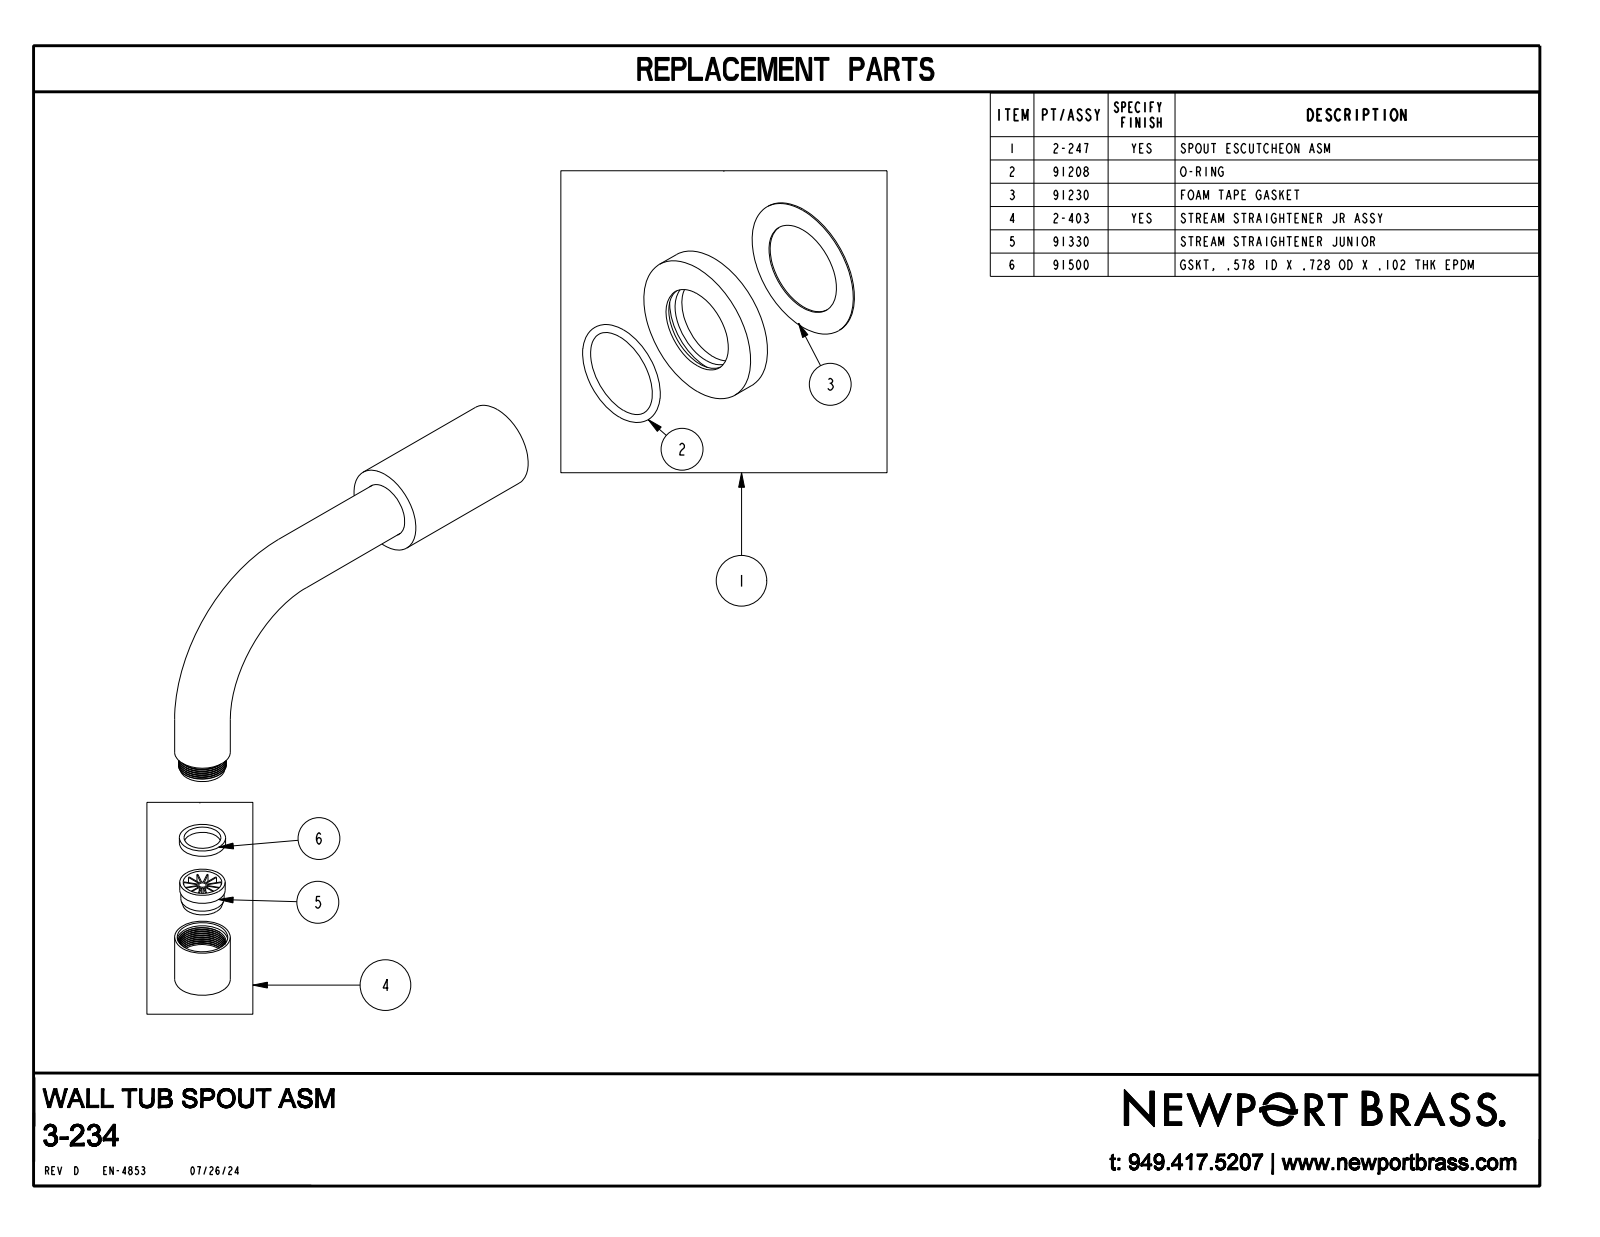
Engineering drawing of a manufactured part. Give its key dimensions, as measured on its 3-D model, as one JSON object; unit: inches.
{"part_name": "10825; 10824; 2-242_ASM; 10663 (+4 more)", "step_written_by": "CREO PARAMETRIC BY PTC INC, 2018400 (AUTOMOTIVE_DESIGN)", "units": "inches", "bodies": {"solids": 4, "faces": 20, "planar": 8, "cylindrical": 10, "other": 2}, "overall_size": [6.998, 4.627, 2.375], "volume_in3": 9.668, "surface_area_in2": 47.46, "round_bosses_or_shafts": [[0.875, 2], [2.375, 1], [1.375, 1]], "face_to_face_distances": [0.375, 1, 1.375, 2.5, 1.5, 1.125, 0.81, 2, 0.625, 0.5]}
